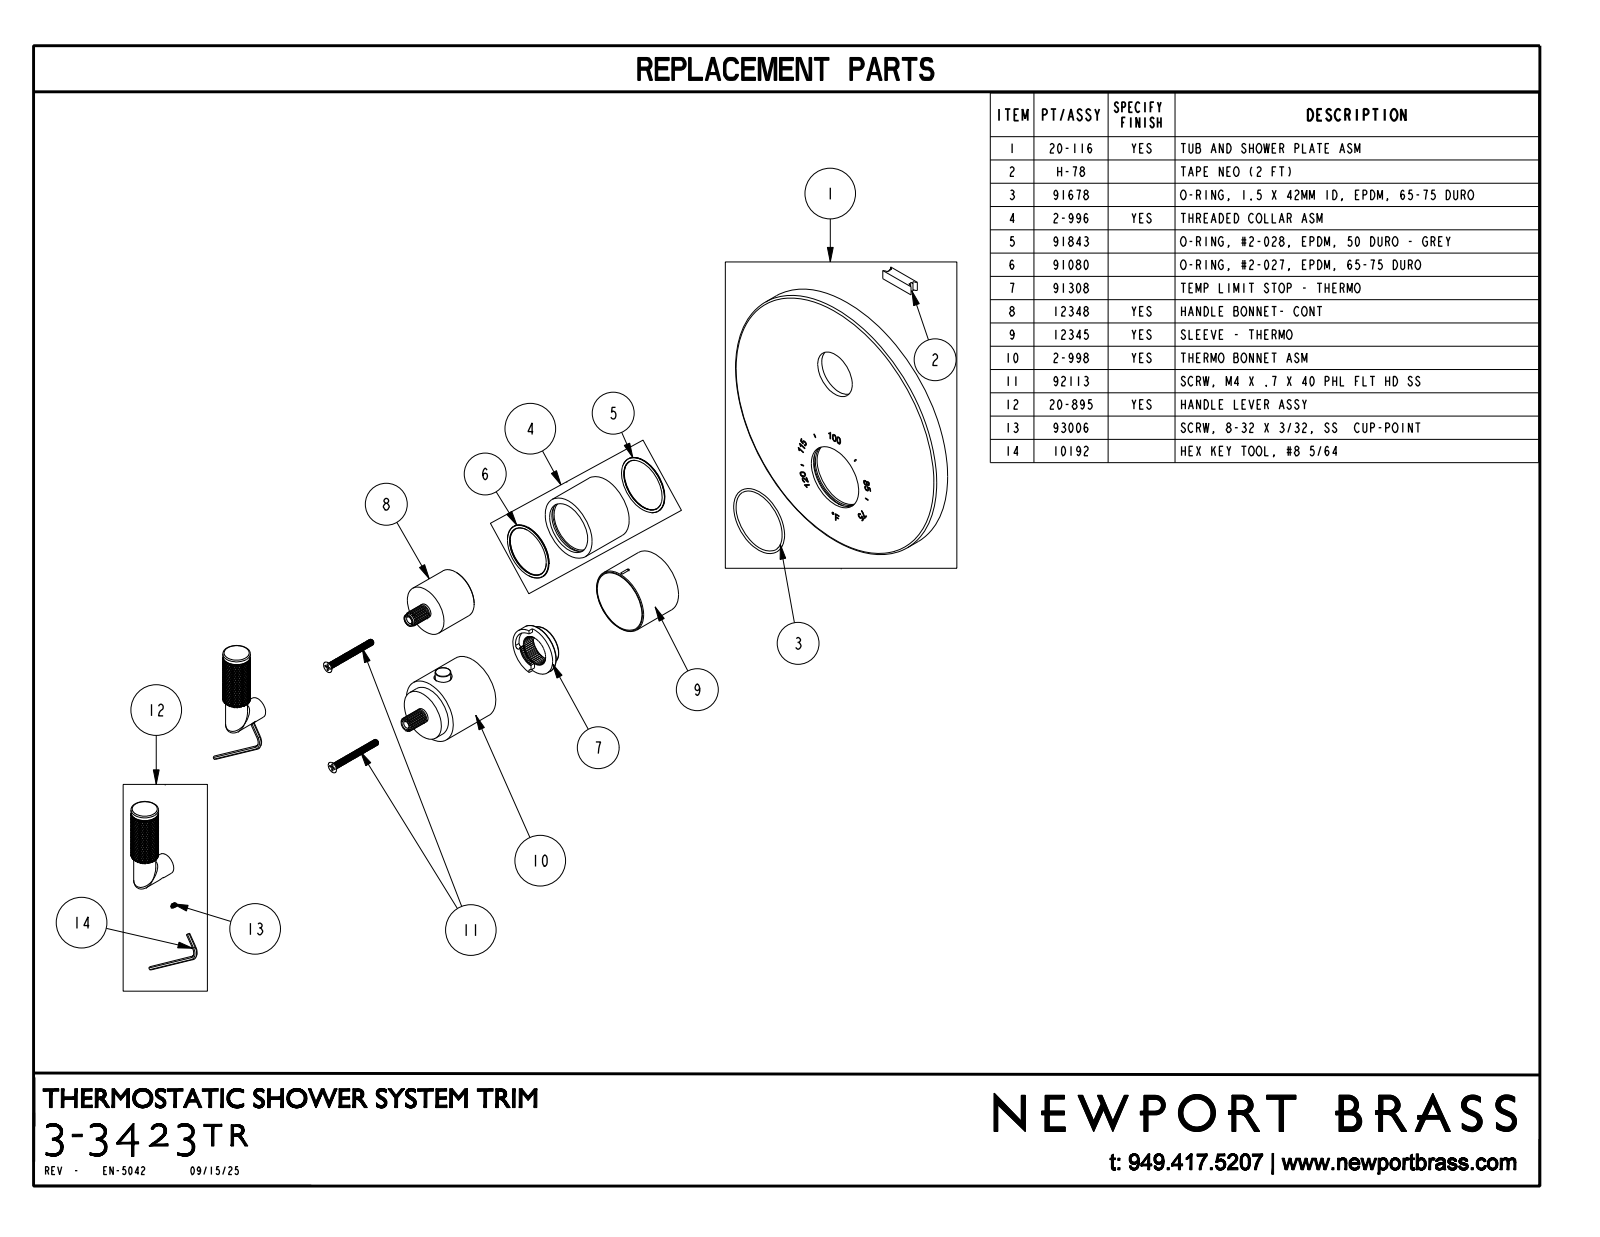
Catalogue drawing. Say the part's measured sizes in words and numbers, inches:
The part is named "3-3423TR". Its 3-D file was written by "CREO PARAMETRIC BY PTC INC, 2025093 (CONFIG_CONTROL_DESIGN)". It is 1 solid with 8310 faces: 158 planar, 1603 cylindrical and 6549 other. Overall it measures 7.17 by 7.09 by 3.554 inches. Its volume is 26.2 cubic inches and its surface area 124.5 square inches. Round holes: 2 of diameter 0.4, 1 of diameter 0.063, 1 of diameter 0.406, 1 of diameter 1.342, 1 of diameter 1.673. Round bosses or shafts: 4 of diameter 0.55, 2 of diameter 1.654, 2 of diameter 0.688, 2 of diameter 0.687, 2 of diameter 0.37, 2 of diameter 0.303, 1 of diameter 7.09, 1 of diameter 1.31. Partial cylindrical surfaces (rounded edges, fillets, slot ends): 1 of radius 0.039, 1 of radius 0.164, 1 of radius 0.756. The main face-to-face distances are 0.438, 0.358, 0.656, 0.218, 2.41, 1.972, 1.754, 0.628, 0.19, 0.028. The hole center spacings are 1.142, 1.144, 3.15, 3.152, 4.292.
